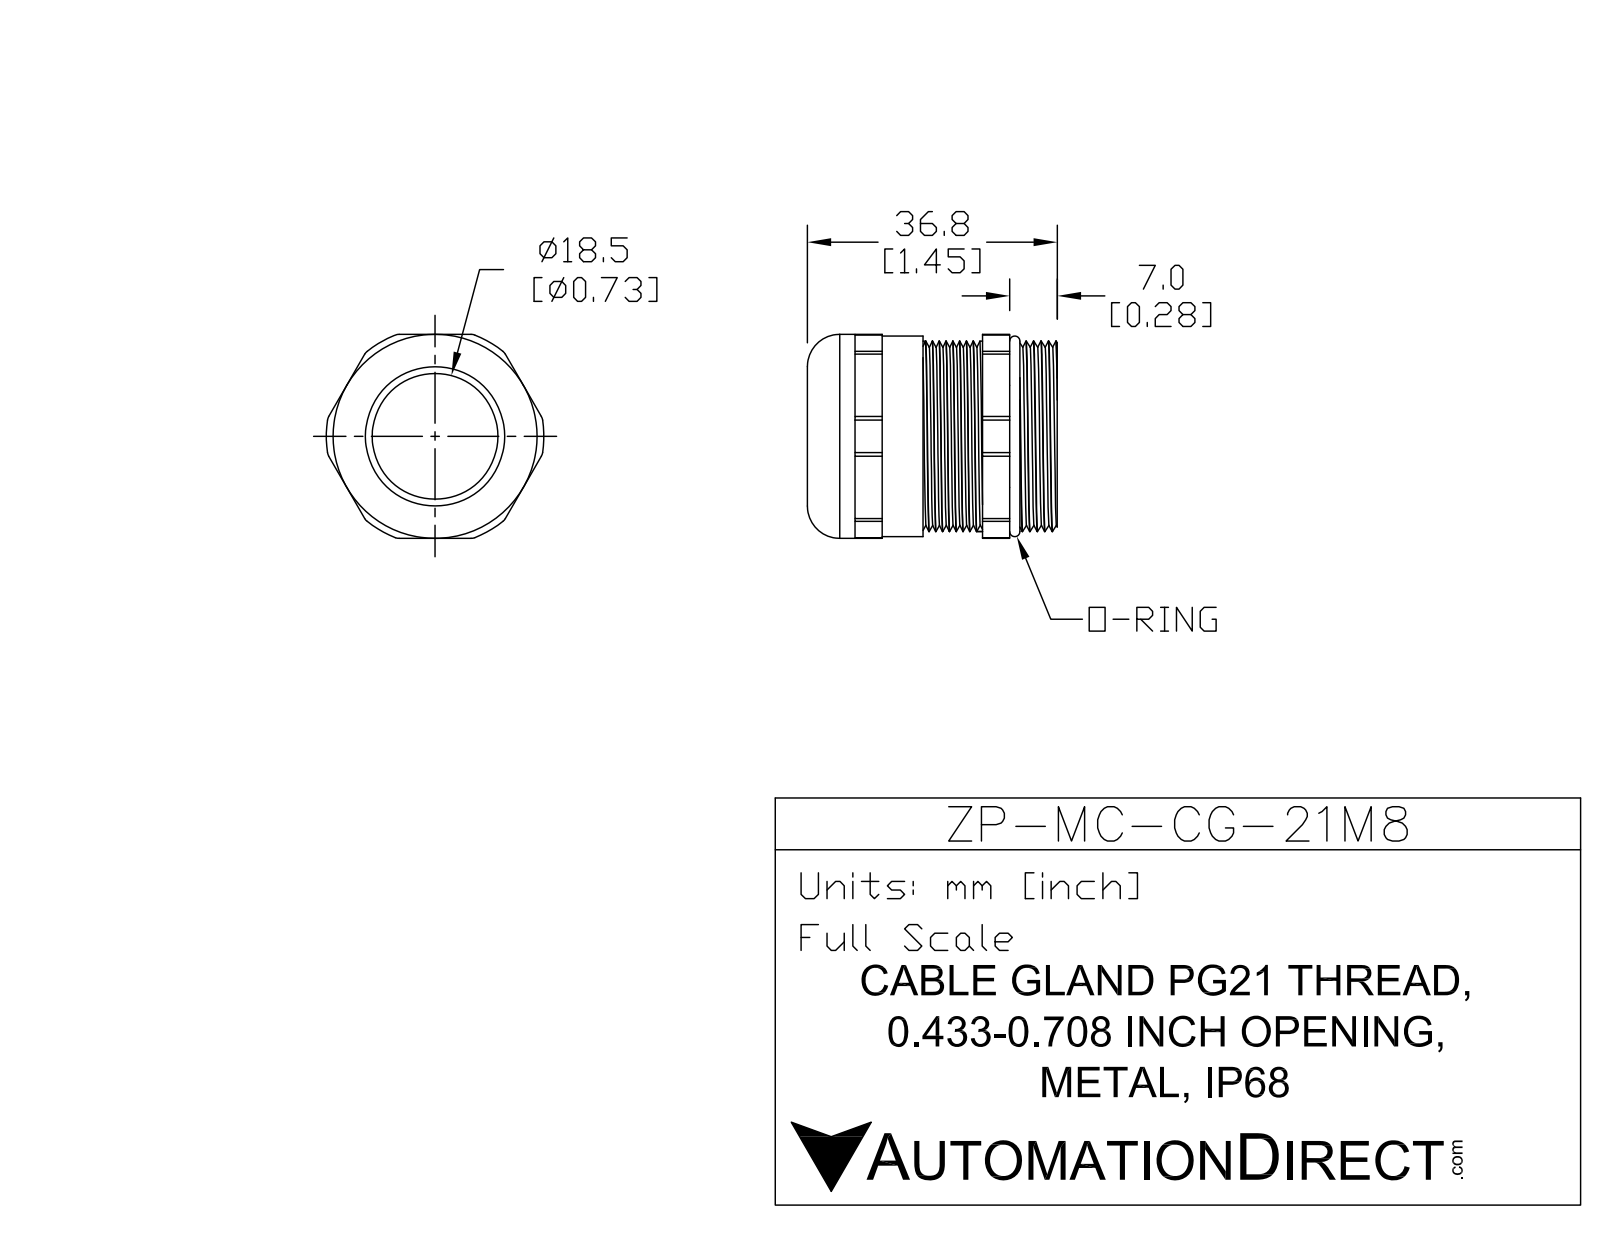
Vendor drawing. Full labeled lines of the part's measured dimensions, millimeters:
Part name (STEP PRODUCT): ZP-MC-CG-21M8
STEP written by: SolidWorks 2011 (AUTOMOTIVE_DESIGN)
Units: millimetres
Bodies: 1 solid, 92 faces (34 planar, 48 cylindrical, 10 other)
Overall size (bounding box): 36.75 × 32 × 30
Volume: 14 105 mm³ · Surface area: 7 959 mm²
Round holes (diameter × count): ⌀18.5 ×1
Round bosses / shafts (diameter × count): ⌀30 ×1, ⌀29.5 ×1, ⌀28 ×1
Partial cylindrical surfaces — rounded edges, fillets, slot ends (radius × count): R1.5 ×12, R14.11 ×1, R14.47 ×1, R16 ×1
Main face-to-face distances: 30, 11, 25.75, 7, 29.75, 4, 18.75, 14.75, 19.75, 8.75
